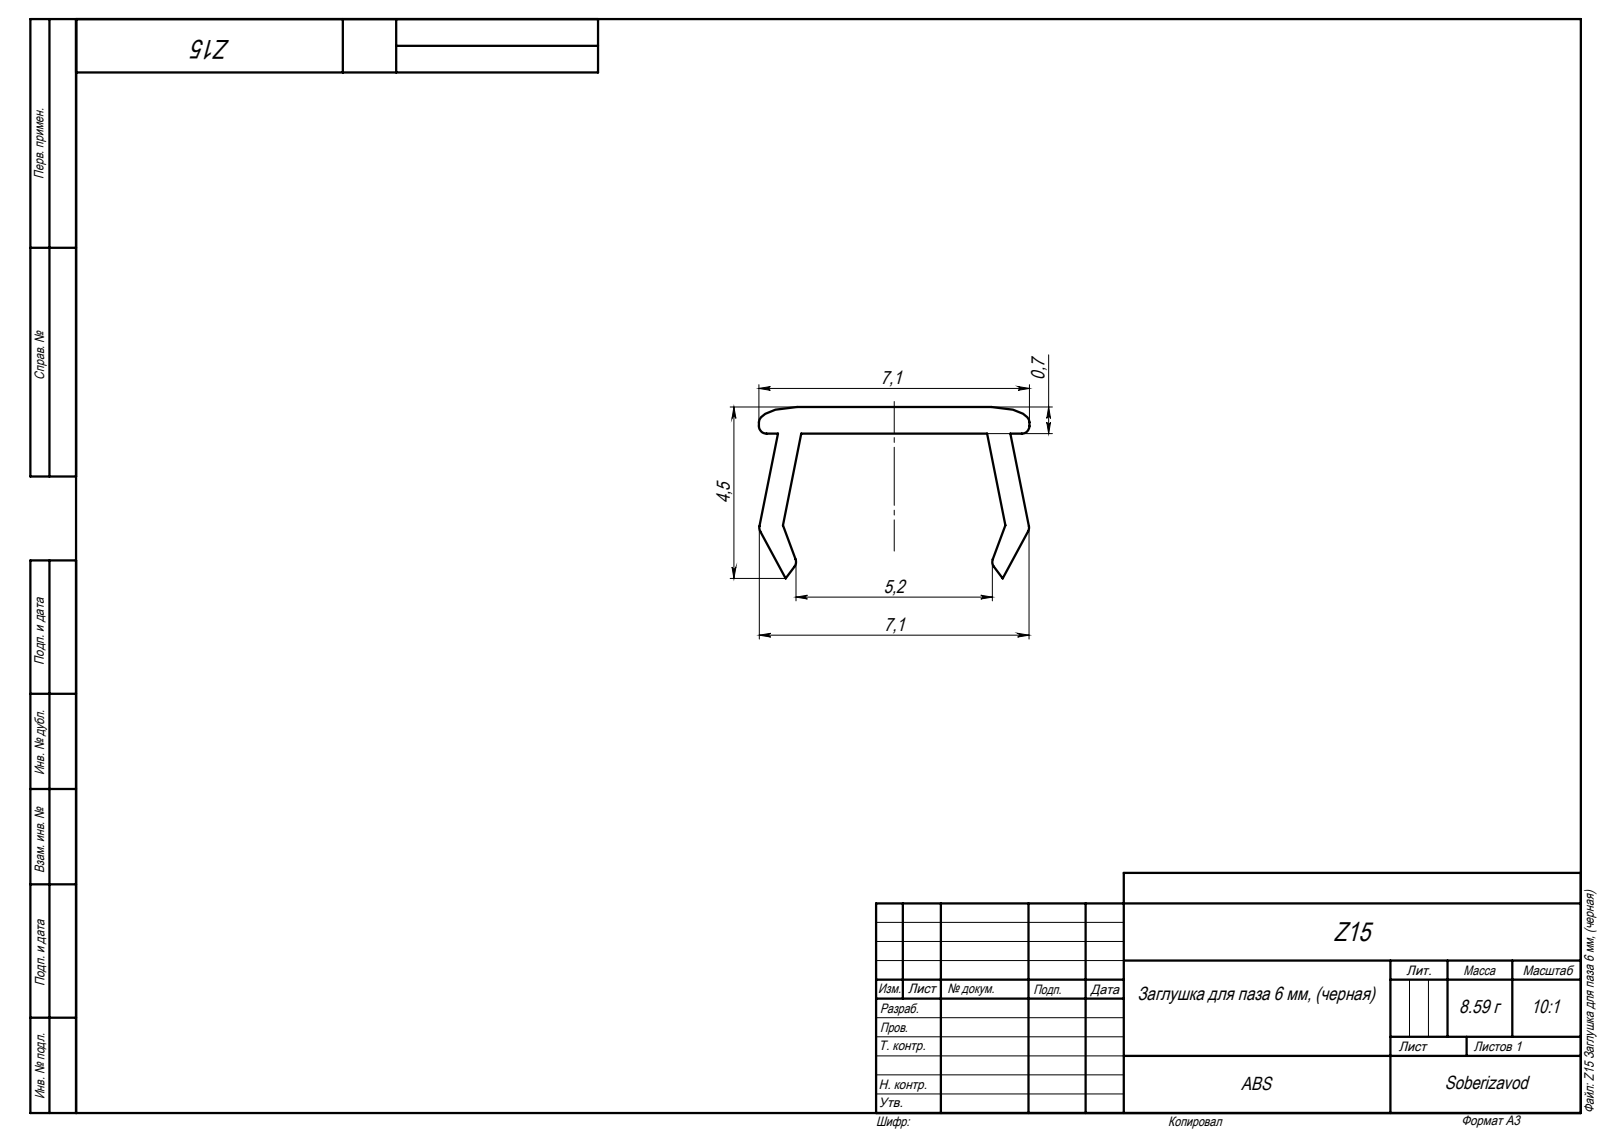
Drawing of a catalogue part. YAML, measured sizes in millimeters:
part_name: "Z15 Заглушка для паза 6 мм, (черная)"
step_written_by: "SolidWorks 2018 (AUTOMOTIVE_DESIGN)"
units: millimeters
bodies: {solids: 1, faces: 28, planar: 18, cylindrical: 8, other: 2}
overall_size: [1000, 7.1, 4.5]
volume: 9108
surface_area: 29756
partial_cylinders:
  - {radius: 0.2, count: 6}
face_to_face_distances: [0.7, 0.6, 7.1, 1000]
